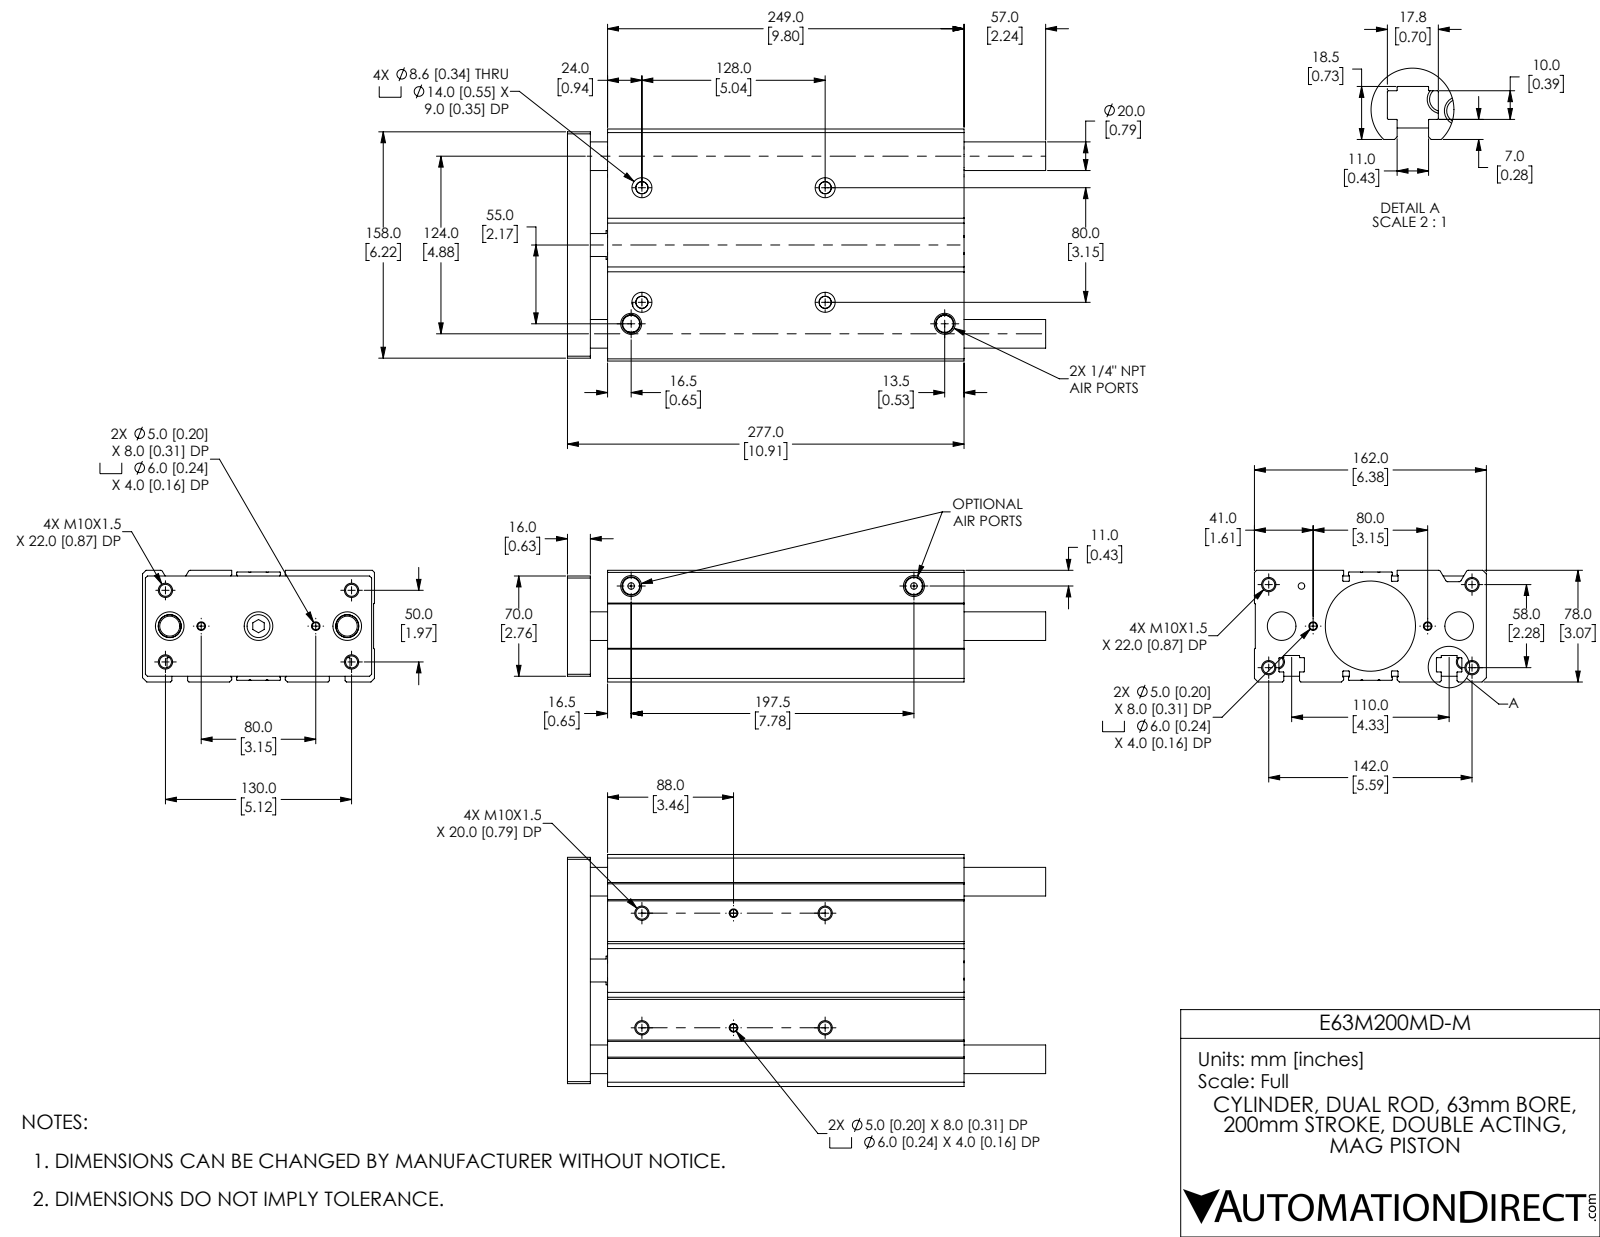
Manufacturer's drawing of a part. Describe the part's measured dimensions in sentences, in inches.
The part is named "E63M200MD-M; E63M200MD-M_ENDPLATE; E63M200MD-M_BODY". Its 3-D file was written by "SolidWorks 2019 (CONFIG_CONTROL_DESIGN)". It is 5 solids with 421 faces: 139 planar, 190 cylindrical and 92 other. Overall it measures 13.15 by 6.378 by 3.071 inches. Its volume is 155 cubic inches and its surface area 595.6 square inches. Round holes: 12 of diameter 0.33, 4 of diameter 0.197, 4 of diameter 0.236, 4 of diameter 0.339, 4 of diameter 0.551, 3 of diameter 0.18, 3 of diameter 0.394, 3 of diameter 0.787, 2 of diameter 0.63, 1 of diameter 0.787, 1 of diameter 2.48, 1 of diameter 2.48. Round bosses or shafts: 1 of diameter 0.63. Partial cylindrical surfaces (rounded edges, fillets, slot ends): 32 of radius 0.008, 28 of radius 0.016, 4 of radius 0.059, 2 of radius 0.012. The main face-to-face distances are 3.071, 0.047, 3.024, 0.024, 1.102, 6.378, 0.157, 0.63, 0.472, 4.331. The hole center spacings are 0.284, 0.991, 1.195, 1.392, 1.671, 2.139, 2.52, 2.742.
